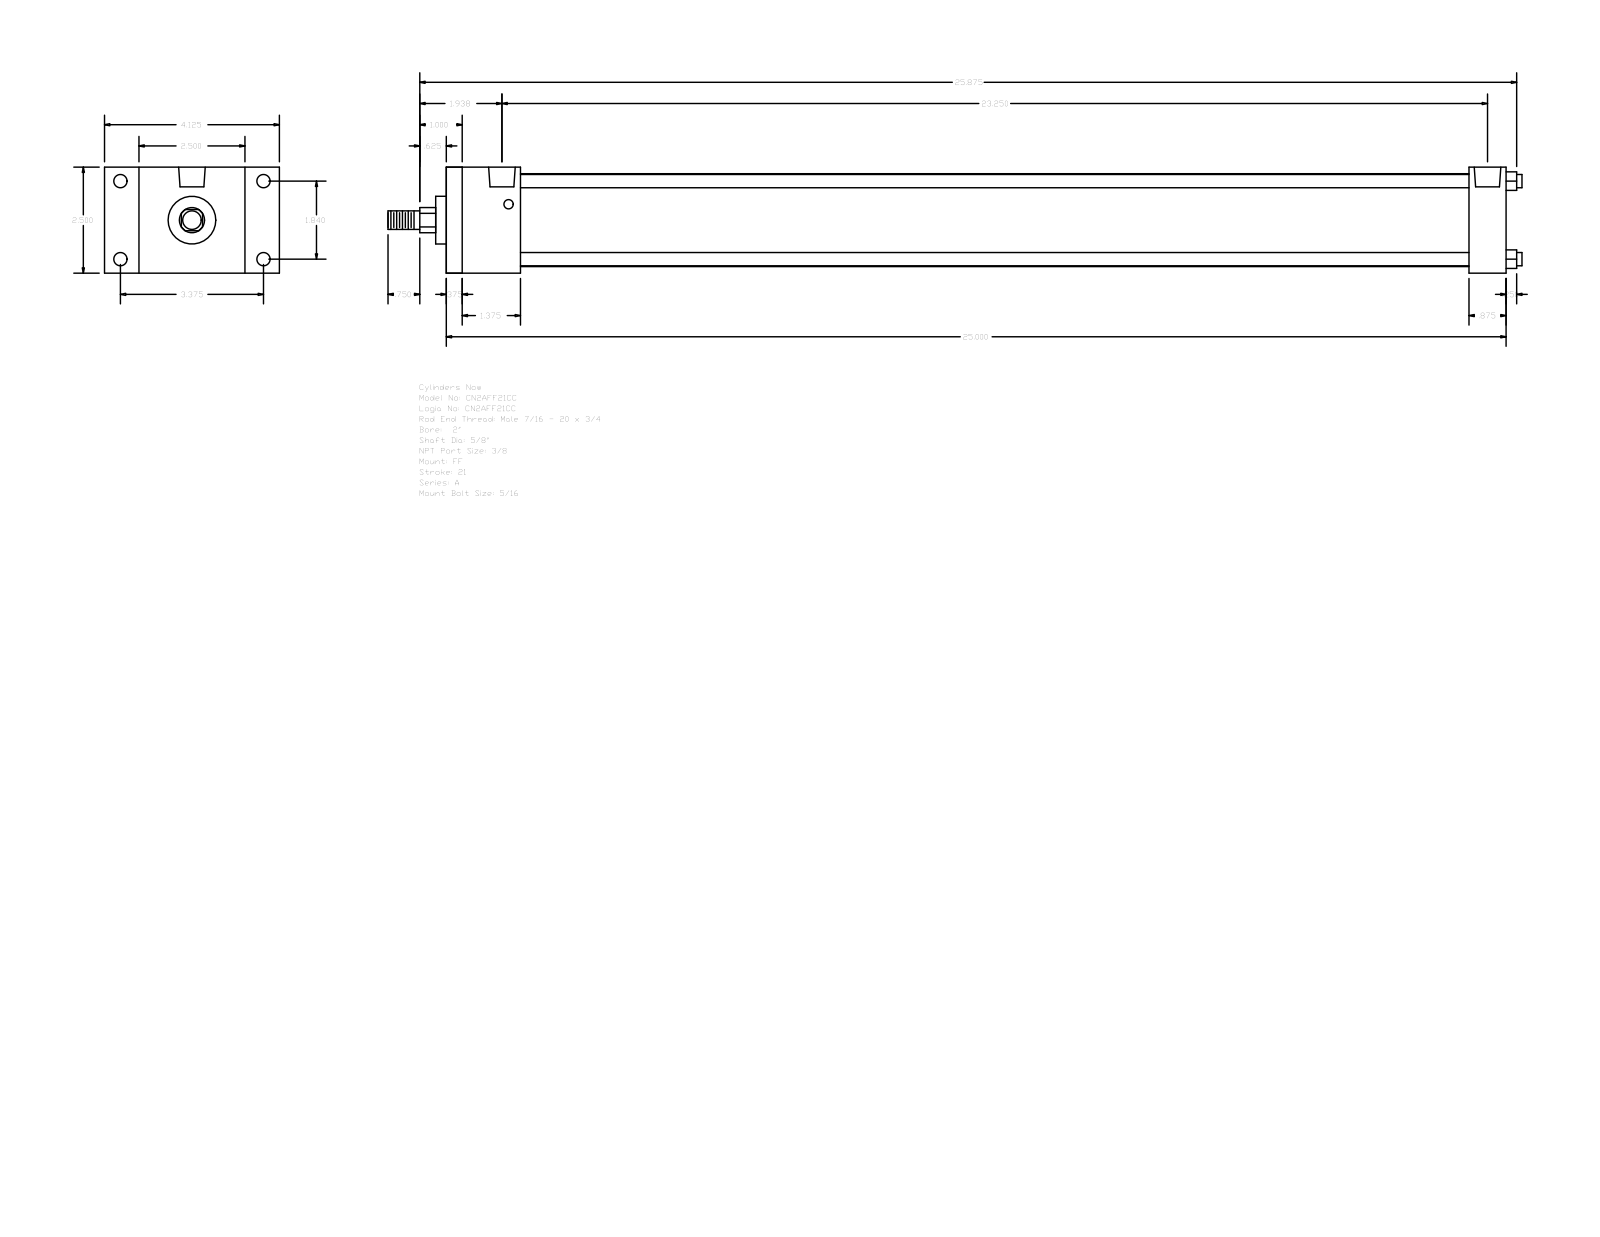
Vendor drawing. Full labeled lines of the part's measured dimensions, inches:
Part name (STEP PRODUCT): A_FF__0200_0.625
STEP written by: GSSL Pune (CONFIG_CONTROL_DESIGN)
Units: inches
Bodies: 0 solids, 92 faces (64 planar, 28 cylindrical, 0 other)
Overall size (bounding box): 26.75 × 4.125 × 2.5
Round holes (diameter × count): ⌀0.219 ×4, ⌀0.313 ×4, ⌀0.627 ×2
Round bosses / shafts (diameter × count): ⌀0.313 ×4, ⌀2.19 ×1, ⌀1.125 ×1, ⌀0.625 ×1, ⌀0.437 ×1
Partial cylindrical surfaces — rounded edges, fillets, slot ends (radius × count): R0.297 ×1
Main face-to-face distances: 2.5, 25, 0.375, 24.625, 1.375, 1.75, 24.125, 23.75, 22.375, 23.25
Hole centre spacings: 1.84, 3.375, 3.844, 22.937, 0.156, 0.157, 23.093, 23.094
